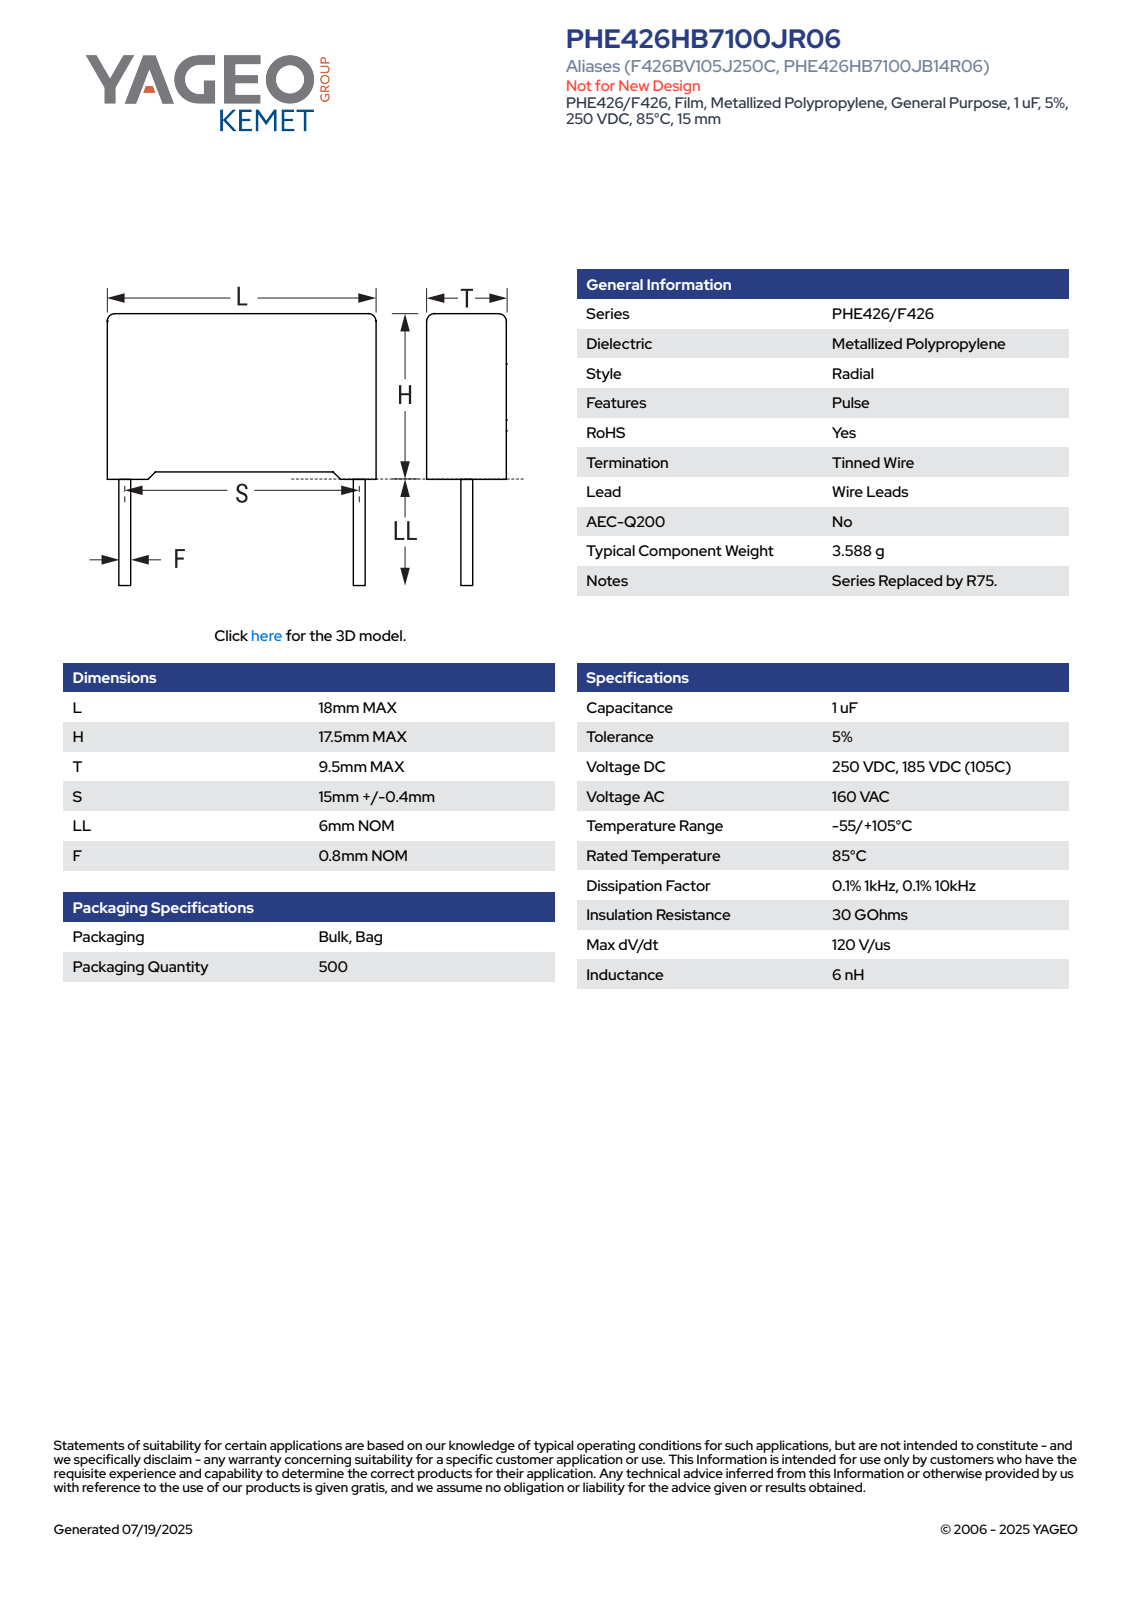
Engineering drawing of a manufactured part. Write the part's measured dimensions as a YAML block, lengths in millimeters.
part_name: "CFR_RB2_18X17.5X9.5_L18H17.5T9.5S15LL6F0.8"
step_written_by: "SolidWorks 2021 (AUTOMOTIVE_DESIGN)"
units: millimeters
bodies: {solids: 4, faces: 85, planar: 77, cylindrical: 8, other: 0}
overall_size: [23.5, 18, 9.51]
volume: 2884
surface_area: 1361
round_bosses_or_shafts:
  - {diameter: 0.8, count: 2}
partial_cylinders:
  - {radius: 0.5, count: 4}
face_to_face_distances: [9.5, 18, 16.75, 0.6, 0.75, 17.5, 16.9, 17.4, 8.9, 16.8]
